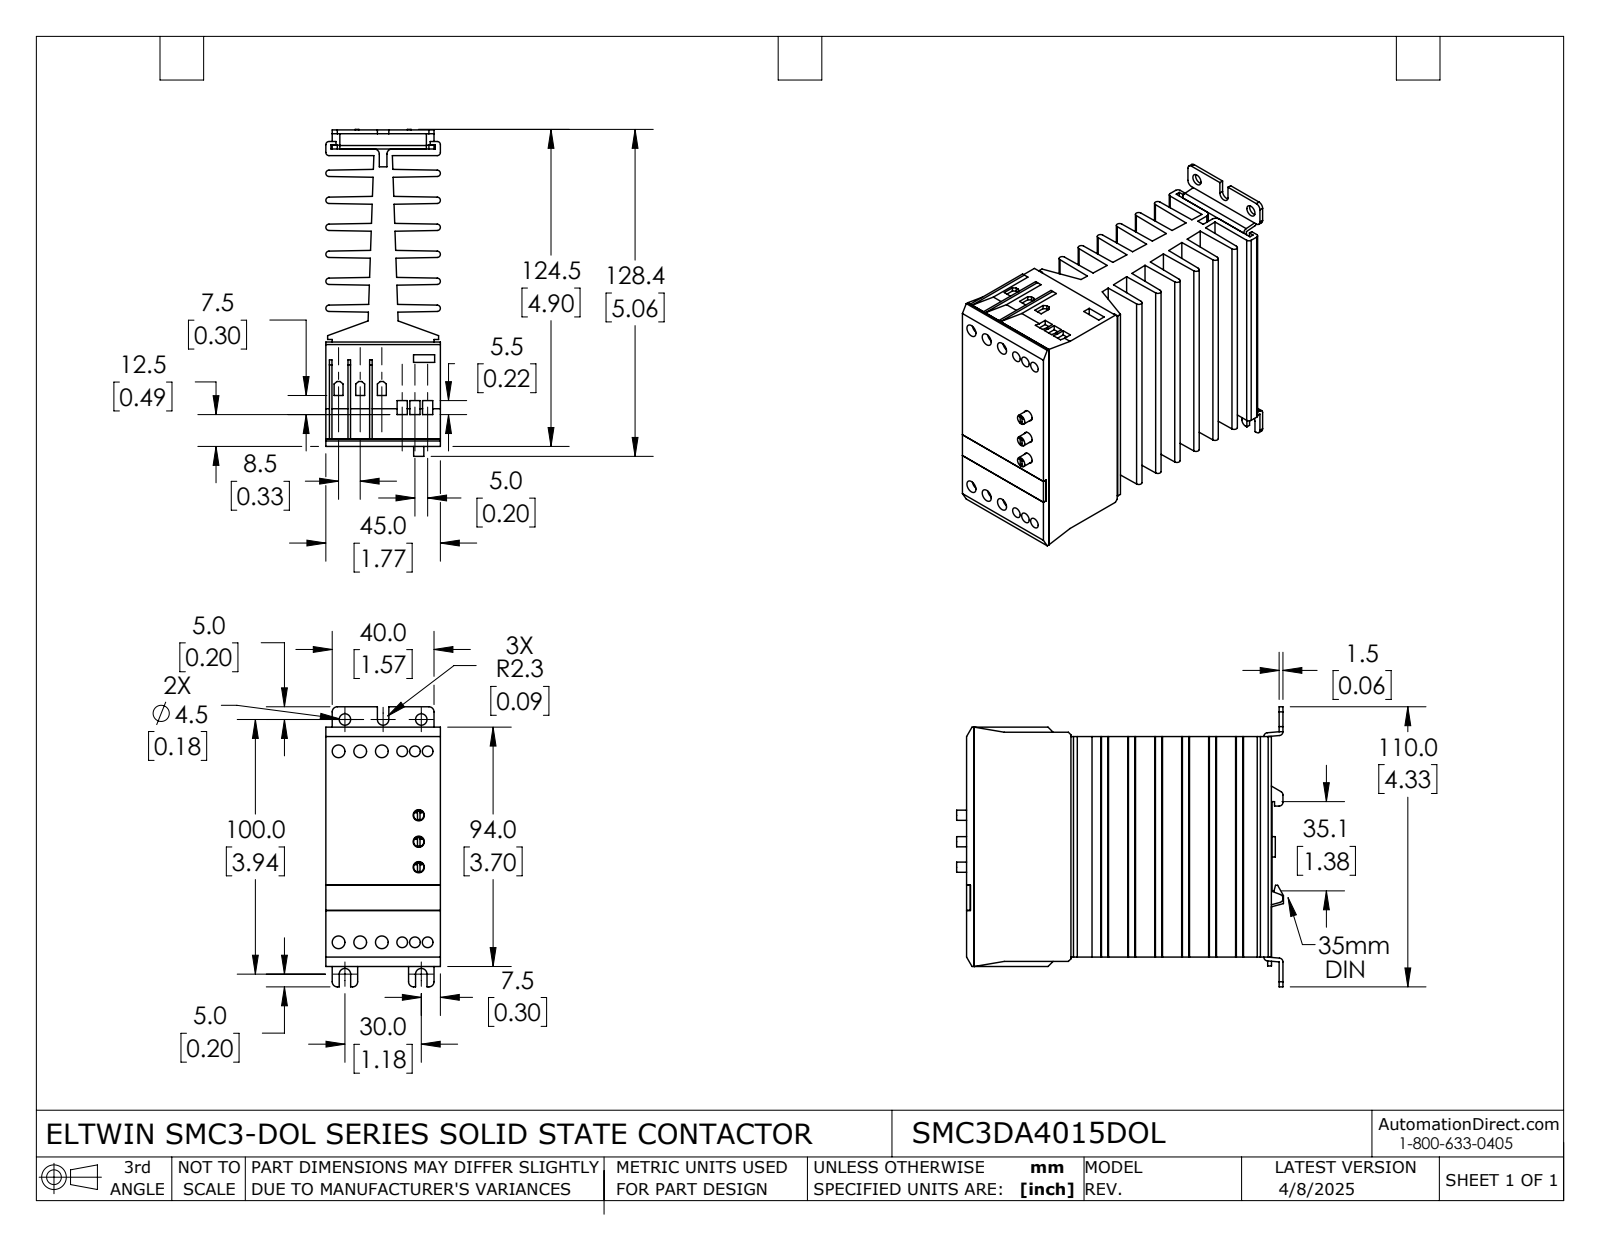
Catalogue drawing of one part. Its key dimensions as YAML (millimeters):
part_name: "SMC3DA4015DOL"
step_written_by: "SolidWorks 2021 (AUTOMOTIVE_DESIGN)"
units: millimeters
bodies: {solids: 8, faces: 473, planar: 348, cylindrical: 123, other: 2}
overall_size: [128.4, 110, 45]
volume: 309400
surface_area: 107400
round_holes:
  - {diameter: 4.4, count: 9}
  - {diameter: 4.2, count: 6}
  - {diameter: 5, count: 6}
  - {diameter: 6, count: 6}
  - {diameter: 4.5, count: 2}
round_bosses_or_shafts:
  - {diameter: 4, count: 3}
  - {diameter: 8, count: 1}
partial_cylinders:
  - {radius: 2, count: 18}
  - {radius: 1.2, count: 16}
  - {radius: 1.5, count: 10}
  - {radius: 1.3, count: 4}
  - {radius: 2.3, count: 3}
face_to_face_distances: [10.6, 21.2, 3.2, 31.8, 7.4, 13.8, 18, 24.4, 42.4, 28.6]
hole_center_spacings: [75, 5, 8.5, 75.2, 75.5, 10, 12.8, 30]
